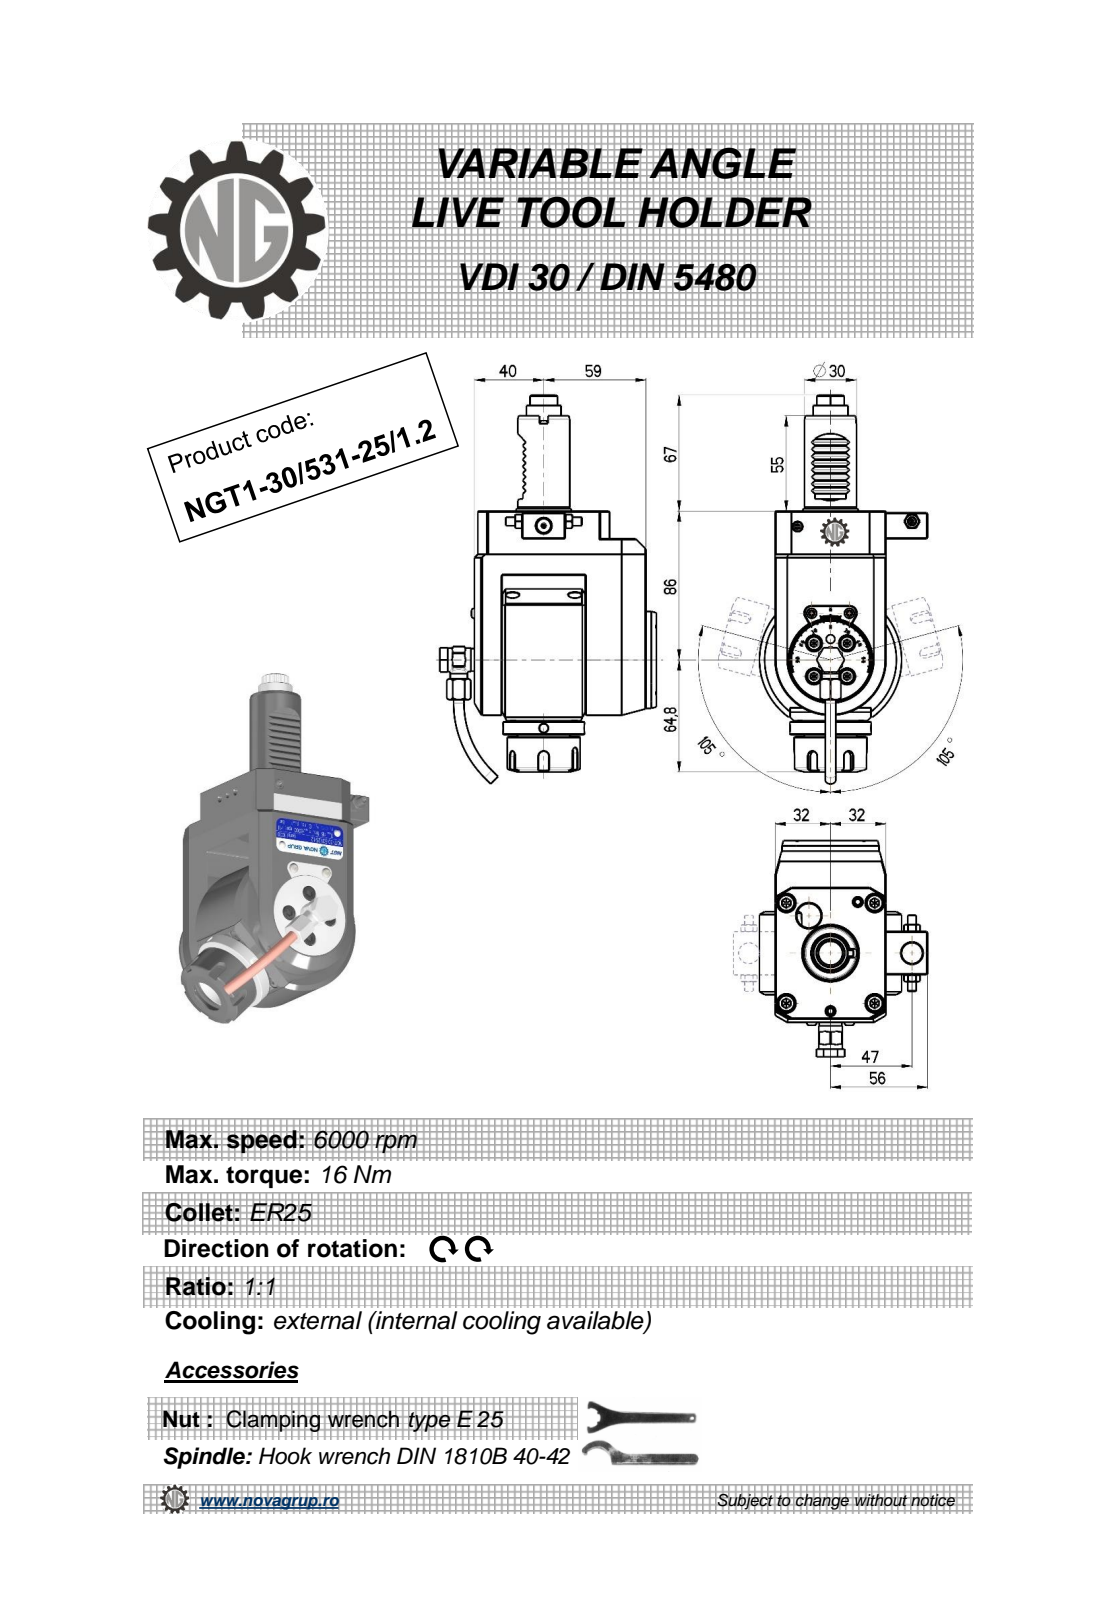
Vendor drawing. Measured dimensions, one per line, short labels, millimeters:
name: NGT1_30_531_25_1_2
written by: PRO/ENGINEER BY PARAMETRIC TECHNOLOGY CORPORATION, 2010280 (CONFIG_CONTROL_DESIGN)
unit: mm
bodies: 1 solid, 643 faces (233 planar, 207 cylindrical, 203 other)
size: 224.67 × 124.9 × 97
volume: 790 116 mm³; area: 76 472 mm²
holes: 3× ⌀4, 2× ⌀5, 1× ⌀3, 1× ⌀4.2, 1× ⌀6.2, 1× ⌀9, 1× ⌀9.5, 1× ⌀11, 1× ⌀12, 1× ⌀20.3
bosses: 2× ⌀10, 2× ⌀6, 2× ⌀5.7, 1× ⌀82, 1× ⌀56, 1× ⌀47, 1× ⌀42, 1× ⌀35
rounds: 36× R1.98, 12× R0.26, 8× R0.3, 6× R0.16, 5× R3, 4× R0.5, 2× R1, 1× R7.29
face distances: 64, 16, 37, 6, 99, 105, 21, 14, 83, 35
hole spacings: 0.4, 39.45, 47, 49, 49.4, 67.9, 68.19, 92.78
